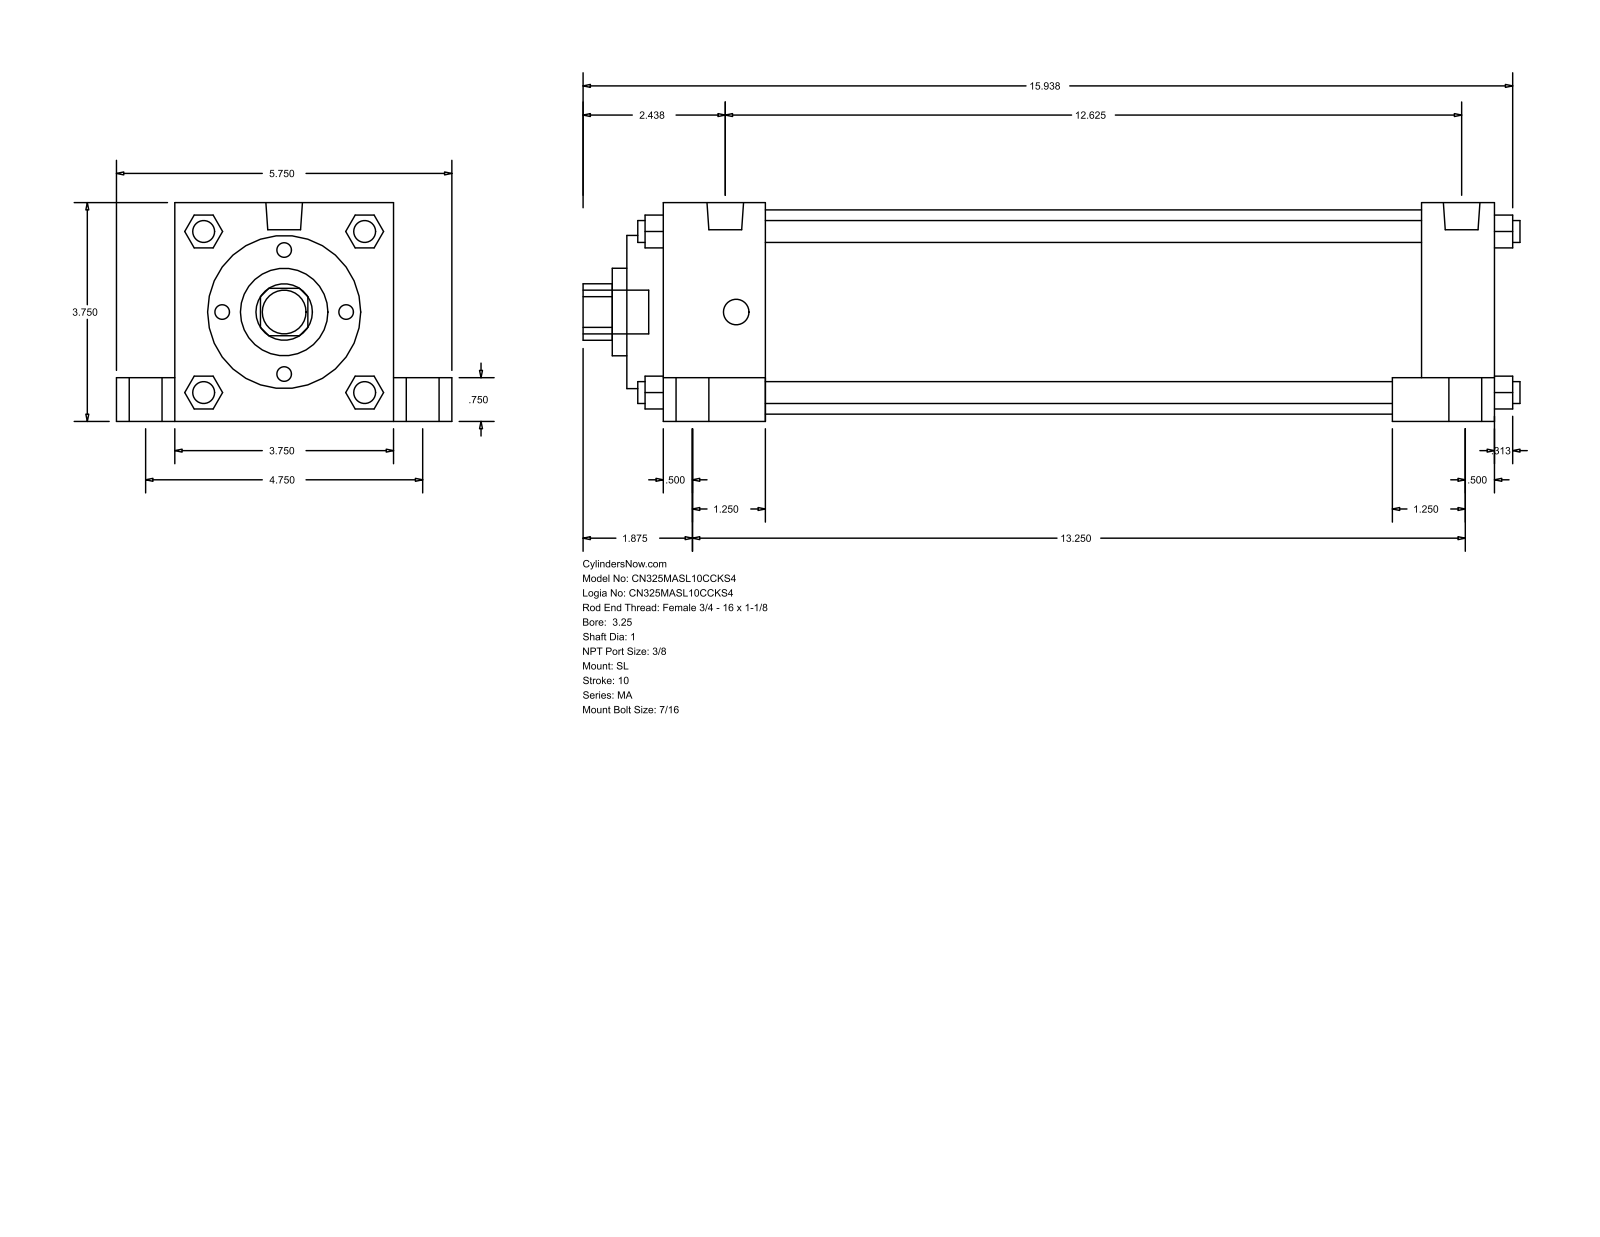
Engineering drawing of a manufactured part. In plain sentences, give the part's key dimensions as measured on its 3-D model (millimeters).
The part is named "MA_SL__0325_1". Its 3-D file was written by "GSSL Pune (CONFIG_CONTROL_DESIGN)". It is 0 solids with 150 faces: 113 planar, 37 cylindrical and 0 other. Overall it measures 407.99 by 146.05 by 95.25 millimeters. Round holes: 1 of diameter 25.4, 1 of diameter 38.1, 1 of diameter 66.67, 1 of diameter 88.9. Round bosses or shafts: 4 of diameter 20.64, 4 of diameter 14.29, 4 of diameter 11.11, 4 of diameter 9.53, 2 of diameter 15.93, 1 of diameter 19.05. Partial cylindrical surfaces (rounded edges, fillets, slot ends): 1 of radius 12.29. The main face-to-face distances are 95.24, 361.96, 15.87, 25.41, 120.65, 19.05, 330.2, 31.76, 44.46, 285.74.
